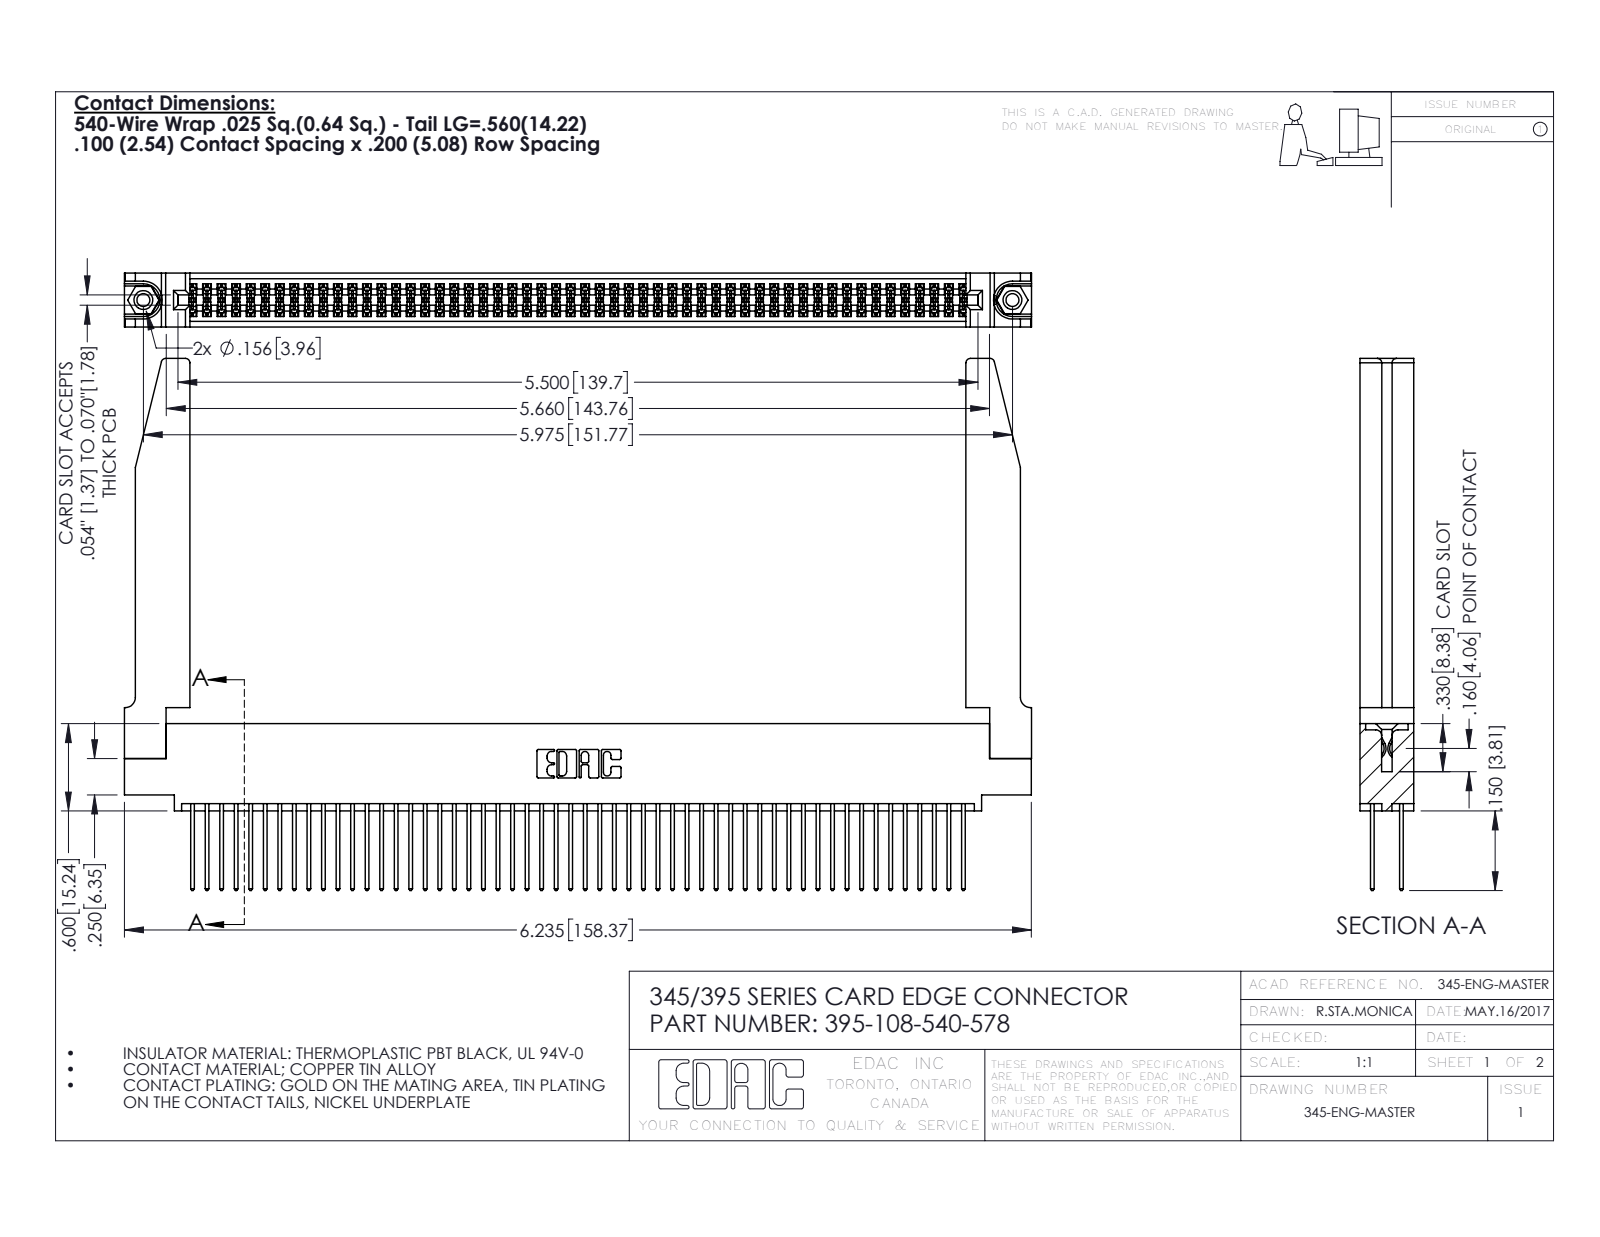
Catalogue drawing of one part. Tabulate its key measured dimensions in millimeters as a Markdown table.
| quantity | value |
| --- | --- |
| part name | 345 Part_0.110 Offset - 0.156 Dia-TH; 345-220-078_345-220-078; 395-108-540-578; 345-250-001_345-250-001-102 (+1 more) |
| STEP written by | SolidWorks 2016 (CONFIG_CONTROL_DESIGN) |
| units | millimeters |
| bodies | 113 solids, 5764 faces (3790 planar, 1922 cylindrical, 52 other) |
| overall size | 158.4 × 92.9 × 9.4 |
| volume | 23 600 mm³ |
| surface area | 32 470 mm² |
| round holes (diameter × count) | 2.3 × 2, 3.2 × 2, 4 × 2, 1.6 × 1 |
| round bosses / shafts (diameter × count) | 3.9 × 2 |
| partial cylindrical surfaces (radius × count) | 0.2 × 162, 0.3 × 108, 0.3 × 22, 0.8 × 8, 0.2 × 6, 0.8 × 6, 0.7 × 3, 0.4 × 2 |
| main face-to-face distances | 1.8, 7.6, 9.4, 5.1, 2.5, 6.9, 0.6, 5.7, 4.4, 3.8 |
| hole center spacings | 6.9, 145.8, 151.8 |
